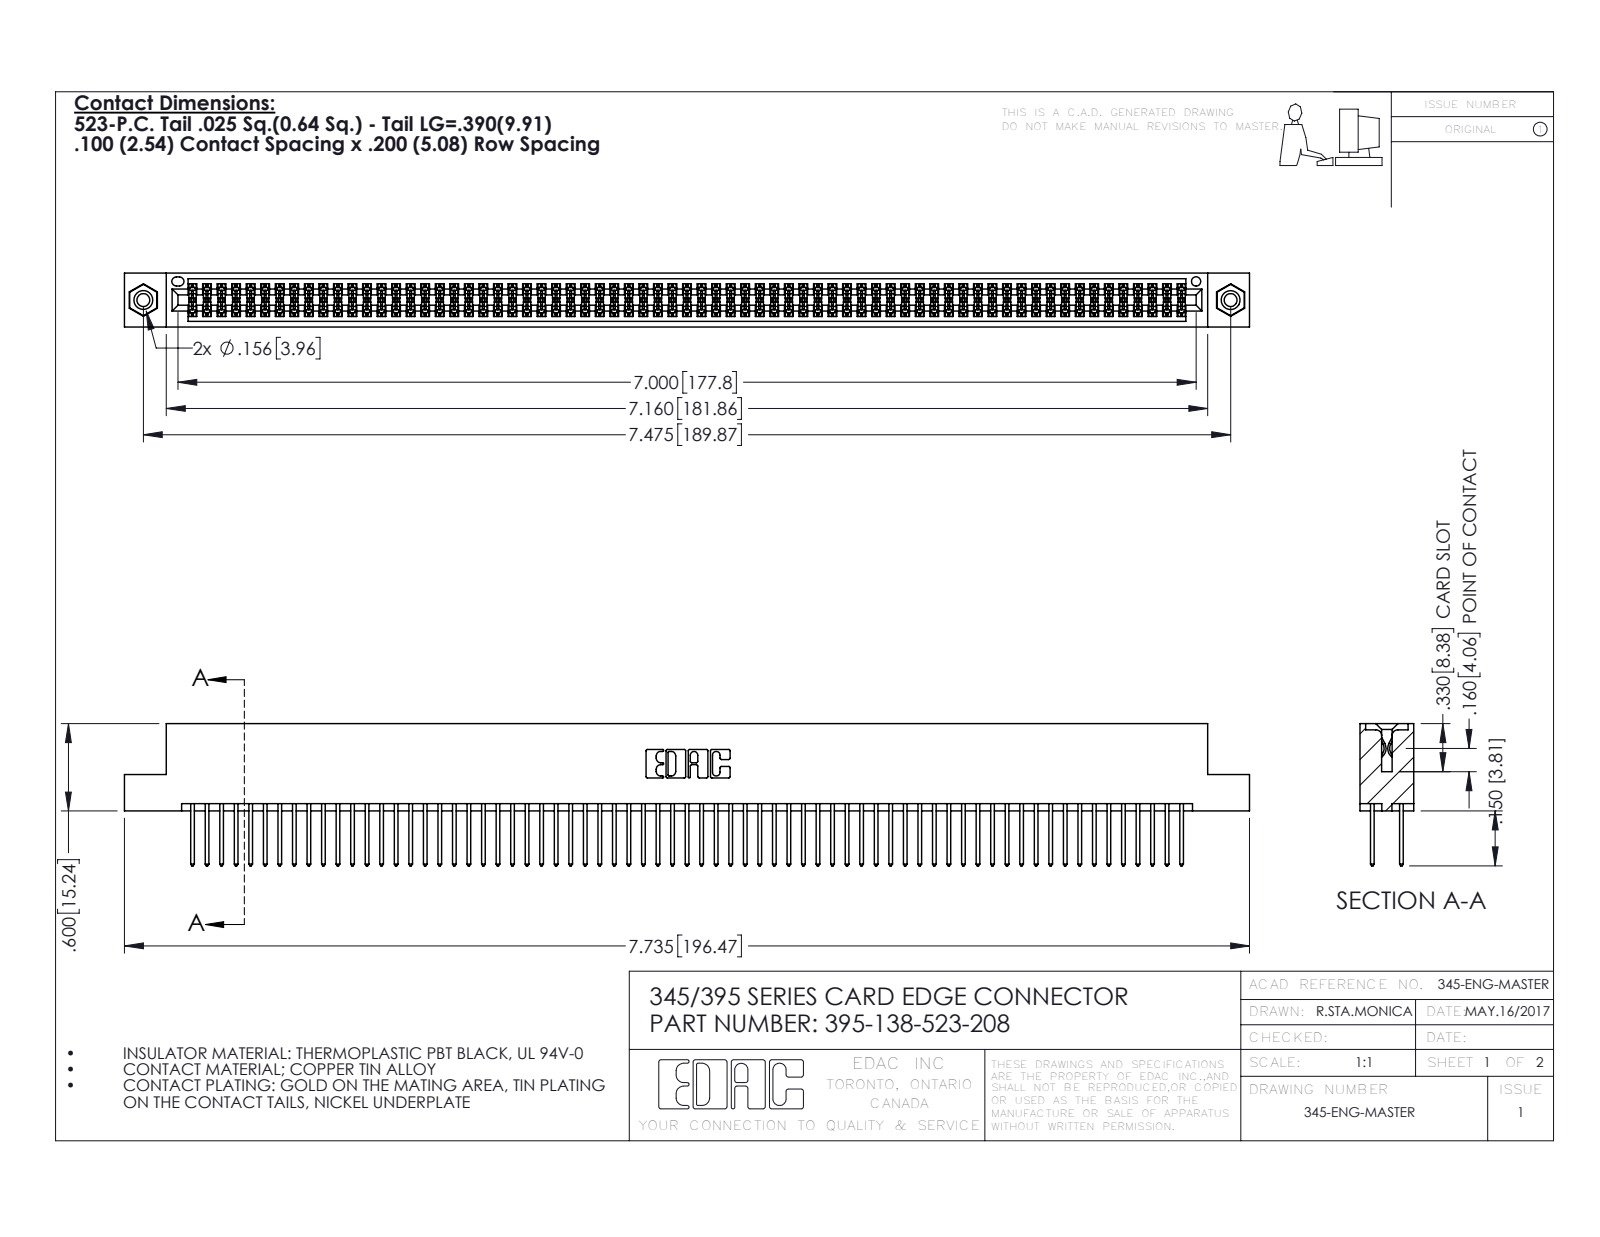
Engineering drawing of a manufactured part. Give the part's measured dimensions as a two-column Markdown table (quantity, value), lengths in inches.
| quantity | value |
| --- | --- |
| part name | 345-292-001_345-293-123; 345-250-001_345-250-003-102; 345 Part_Flush Mounting Lugs - 0.156 Dia-TI; 395-138-523-208 |
| STEP written by | SolidWorks 2016 (CONFIG_CONTROL_DESIGN) |
| units | inches |
| bodies | 141 solids, 7086 faces (4666 planar, 2404 cylindrical, 16 other) |
| overall size | 7.735 × 0.977 × 0.37 |
| volume | 1.197 in³ |
| surface area | 47.73 in² |
| round holes (diameter × count) | 0.089 × 2, 0.125 × 2, 0.156 × 2, 0.064 × 1 |
| round bosses / shafts (diameter × count) | 0.155 × 2 |
| partial cylindrical surfaces (radius × count) | 0.006 × 207, 0.01 × 138, 0.01 × 22, 0.007 × 6, 0.031 × 6, 0.026 × 3, 0.014 × 2, 0.019 × 2 |
| main face-to-face distances | 0.072, 0.298, 0.2, 0.098, 0.272, 0.025, 0.37, 0.225, 0.175, 0.149 |
| hole center spacings | 0.27, 7.239, 7.475 |
